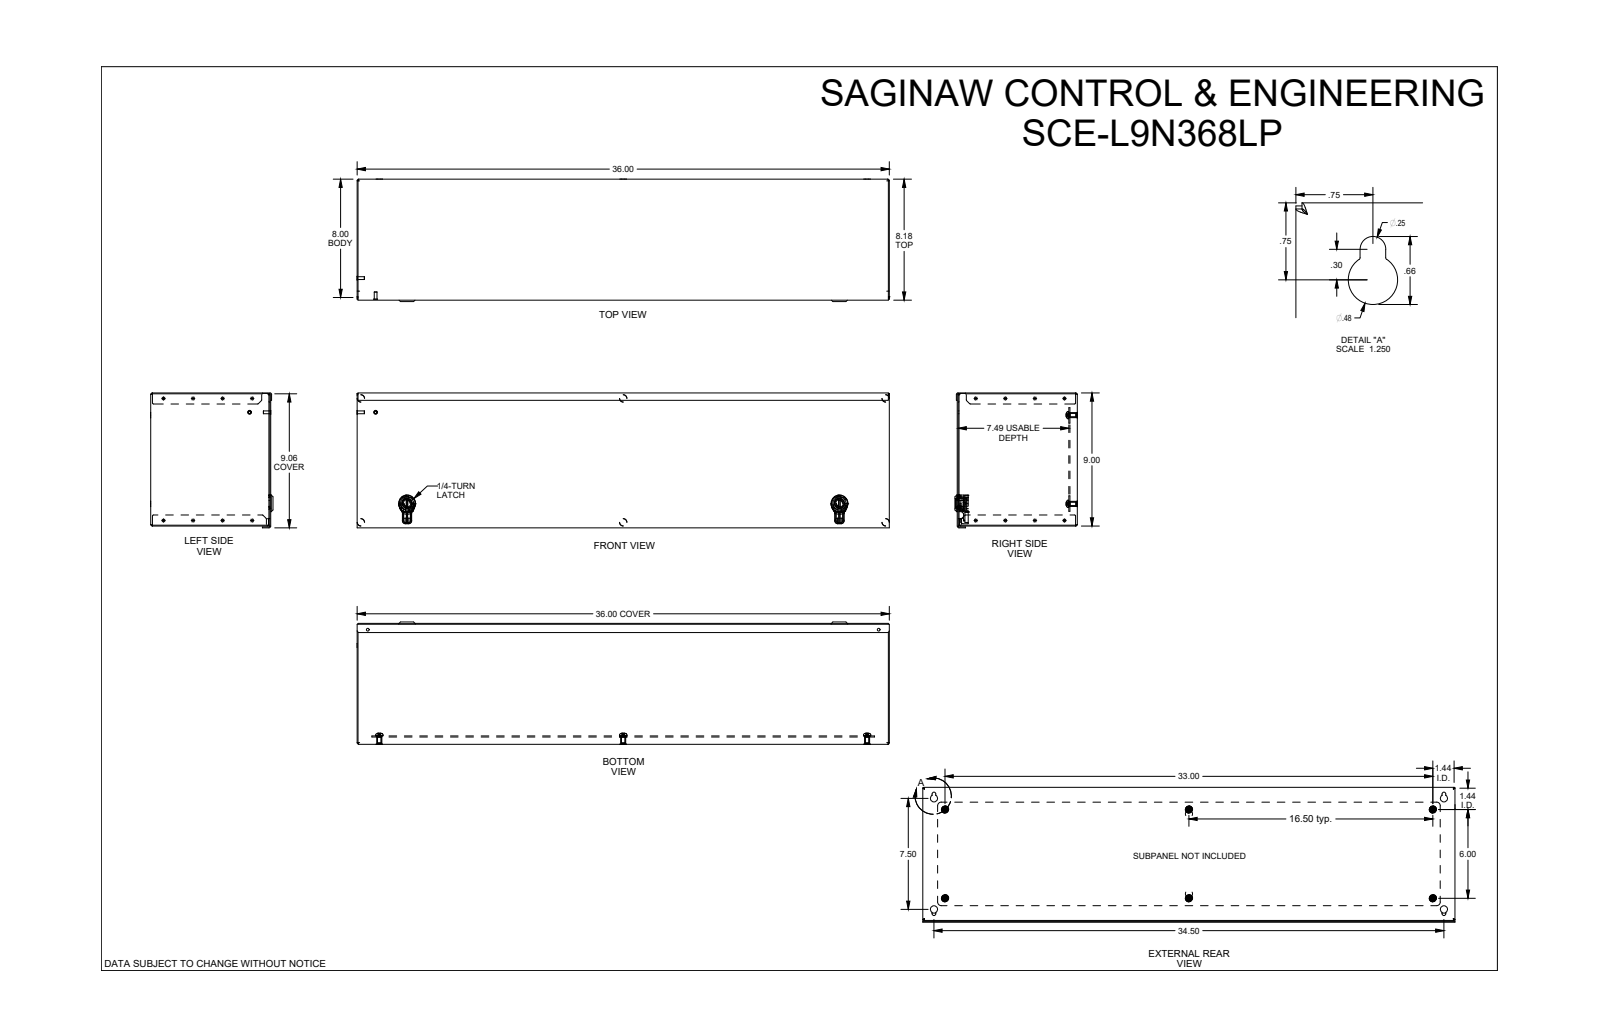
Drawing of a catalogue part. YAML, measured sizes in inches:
part_name: "SCE-L9N368LP"
step_written_by: "SolidWorks 2019 (CONFIG_CONTROL_DESIGN)"
units: inches
bodies: {solids: 27, faces: 1733, planar: 736, cylindrical: 709, other: 288}
overall_size: [36.004, 9.123, 8.281]
volume: 106.7
surface_area: 3445
round_holes:
  - {diameter: 0.25, count: 6}
  - {diameter: 0.343, count: 6}
  - {diameter: 0.281, count: 4}
  - {diameter: 0.48, count: 4}
  - {diameter: 0.188, count: 2}
  - {diameter: 0.193, count: 2}
  - {diameter: 0.44, count: 2}
  - {diameter: 0.635, count: 2}
  - {diameter: 0.891, count: 2}
round_bosses_or_shafts:
  - {diameter: 0.5, count: 6}
  - {diameter: 0.492, count: 6}
  - {diameter: 0.341, count: 6}
  - {diameter: 0.248, count: 6}
  - {diameter: 1.125, count: 2}
  - {diameter: 1.125, count: 2}
  - {diameter: 0.74, count: 2}
  - {diameter: 0.62, count: 2}
partial_cylinders:
  - {radius: 0.01, count: 362}
  - {radius: 0.015, count: 22}
  - {radius: 0.02, count: 16}
  - {radius: 0.052, count: 12}
  - {radius: 0.055, count: 12}
  - {radius: 0.06, count: 12}
  - {radius: 0.112, count: 12}
  - {radius: 0.125, count: 10}
face_to_face_distances: [0.06, 8.94, 0.06, 8, 8.12, 8.06, 8.06, 8.88, 9, 7.565]
hole_center_spacings: [1.061, 6.792, 16.5, 17.266, 17.557, 18.524, 33.758, 34.419]
